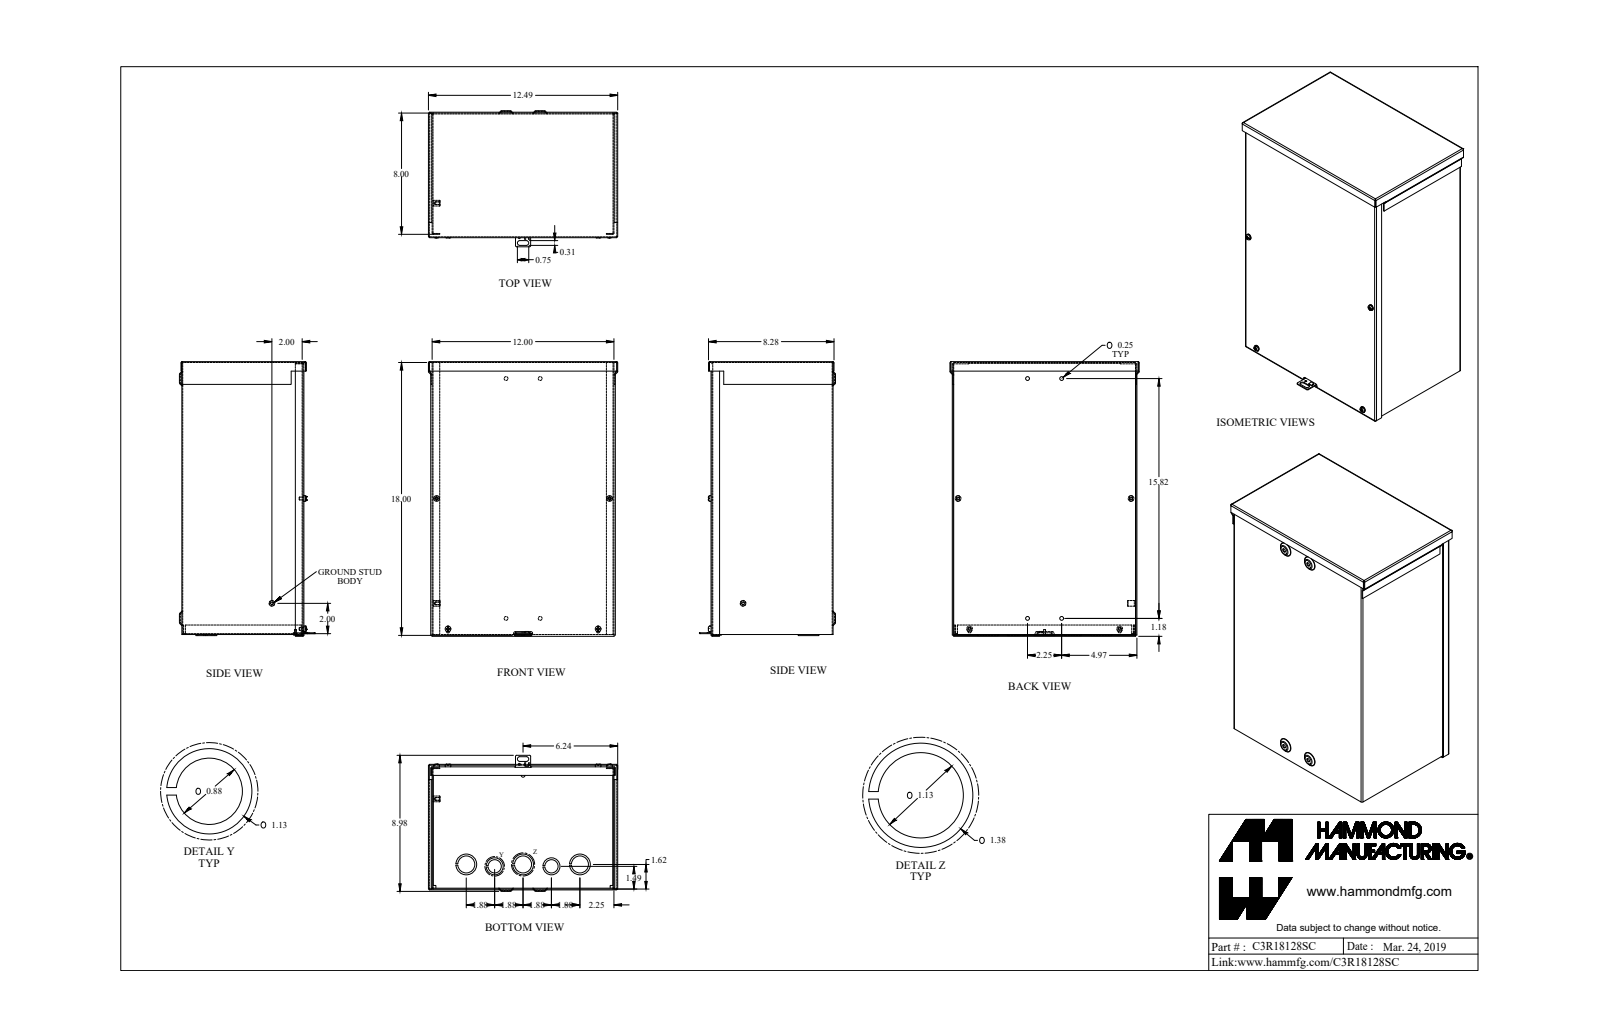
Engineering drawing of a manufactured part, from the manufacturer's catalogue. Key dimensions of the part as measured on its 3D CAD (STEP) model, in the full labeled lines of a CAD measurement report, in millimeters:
Part name (STEP PRODUCT): C3R18128SC_Default
STEP written by: SolidWorks 2019 (CONFIG_CONTROL_DESIGN)
Units: millimetres
Bodies: 11 solids, 429 faces (226 planar, 117 cylindrical, 86 other)
Overall size (bounding box): 460.2 × 317.2 × 228
Volume: 953 100 mm³ · Surface area: 1 324 000 mm²
Round holes (diameter × count): ⌀4.3 ×4, ⌀6.4 ×4, ⌀28.6 ×3, ⌀22.2 ×2, ⌀3.2 ×1, ⌀3.5 ×1, ⌀4 ×1
Round bosses / shafts (diameter × count): ⌀4.8 ×4, ⌀34.9 ×3, ⌀9.5 ×3, ⌀28.6 ×2, ⌀9.5 ×2, ⌀3.2 ×1
Partial cylindrical surfaces — rounded edges, fillets, slot ends (radius × count): R0.7 ×21, R2.2 ×21, R2.8 ×8, R3.2 ×8, R4 ×2
Main face-to-face distances: 1.4, 203.2, 303.4, 201.8, 204.6, 304.8, 301.9, 1.4, 454.3, 455.8
Hole centre spacings: 232.2, 265.5, 95.3, 47.7, 47.8, 57.2, 99.6, 156
